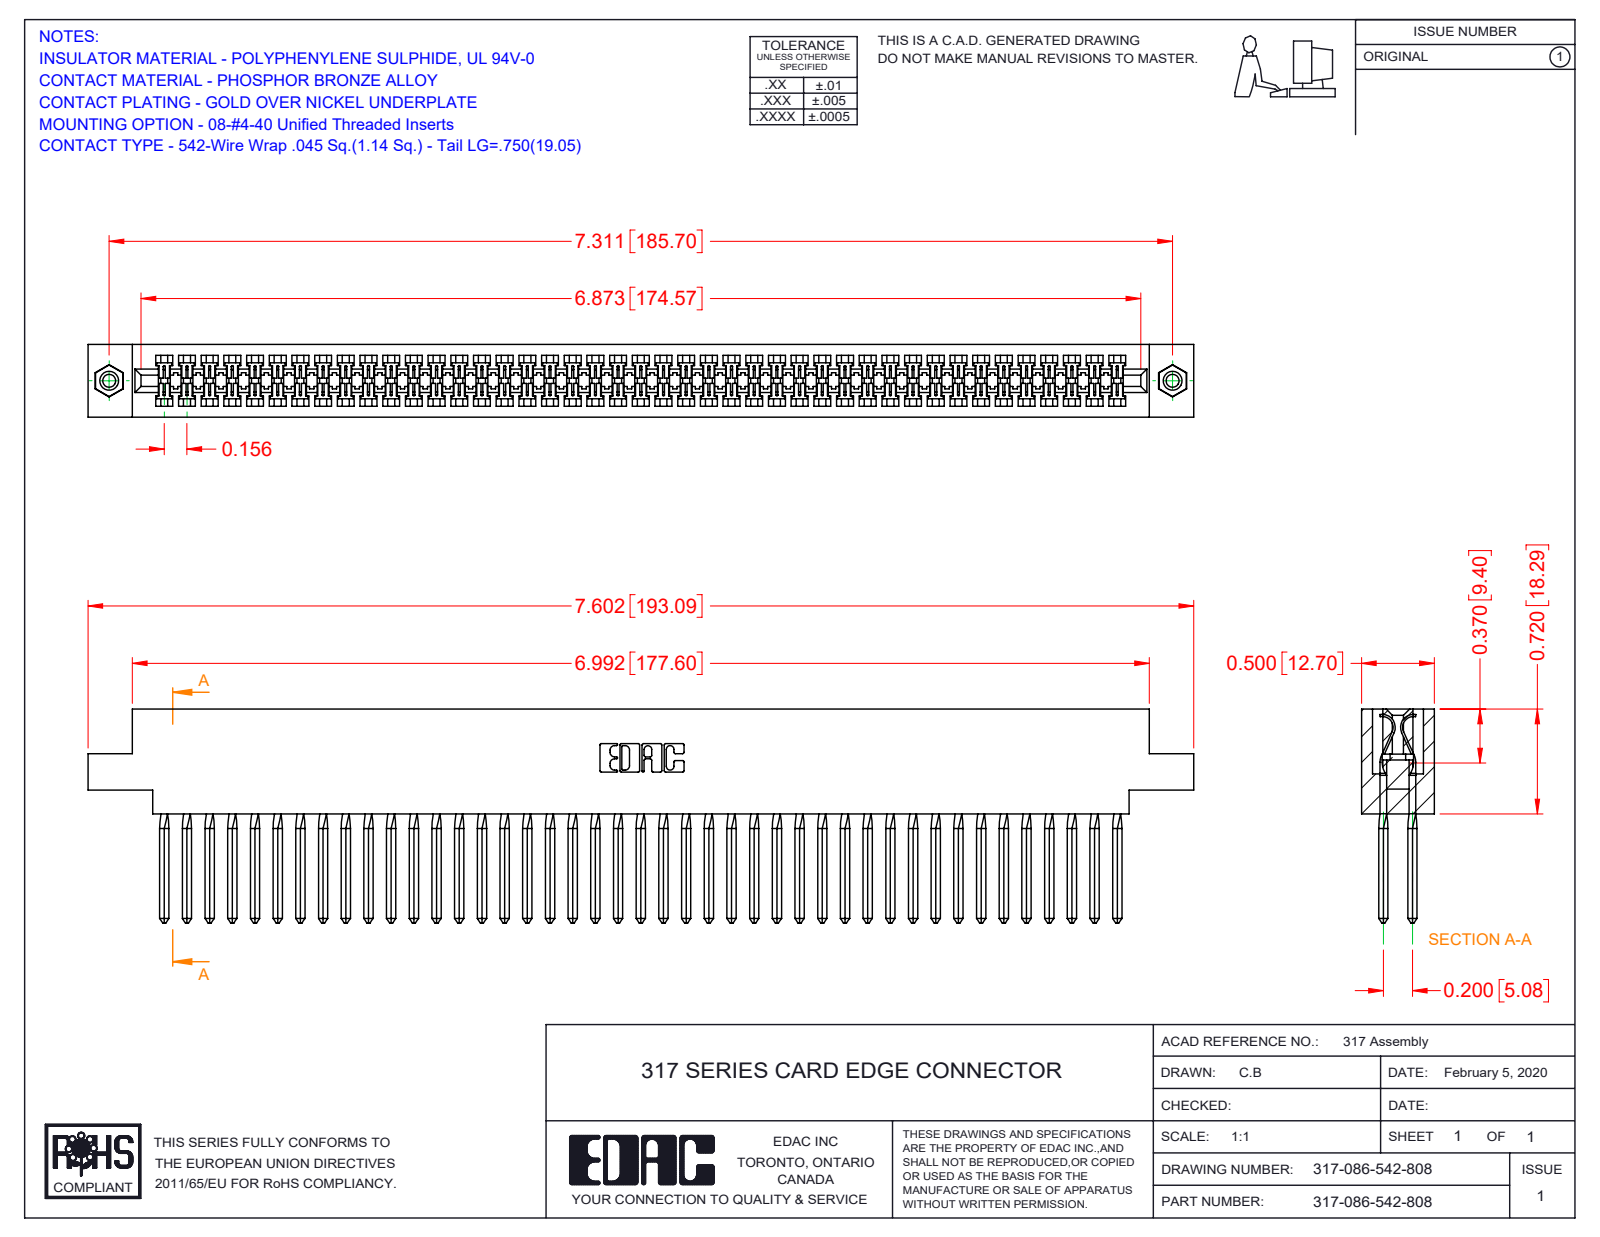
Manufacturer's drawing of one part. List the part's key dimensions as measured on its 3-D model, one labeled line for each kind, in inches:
Part name (STEP PRODUCT): 345-250-001_345-250-003-102; 317-290-003_542; 317 Part_.156 Dia - TI; 317-086-542-808
STEP written by: SolidWorks 2016 (CONFIG_CONTROL_DESIGN)
Units: inches
Bodies: 89 solids, 5064 faces (4046 planar, 658 cylindrical, 360 other)
Overall size (bounding box): 7.602 × 1.47 × 0.5
Volume: 1.931 in³ · Surface area: 68.29 in²
Round holes (diameter × count): ⌀0.089 ×2, ⌀0.125 ×2, ⌀0.156 ×2
Round bosses / shafts (diameter × count): ⌀0.155 ×2
Partial cylindrical surfaces — rounded edges, fillets, slot ends (radius × count): R0.006 ×172, R0.01 ×22, R0.007 ×6, R0.031 ×6, R0.026 ×3, R0.074 ×2, R0.089 ×2, R0.1 ×2
Main face-to-face distances: 0.5, 0.075, 0.425, 0.35, 0.2, 0.046, 0.128, 0.372, 0.052, 0.297
Hole centre spacings: 7.311
